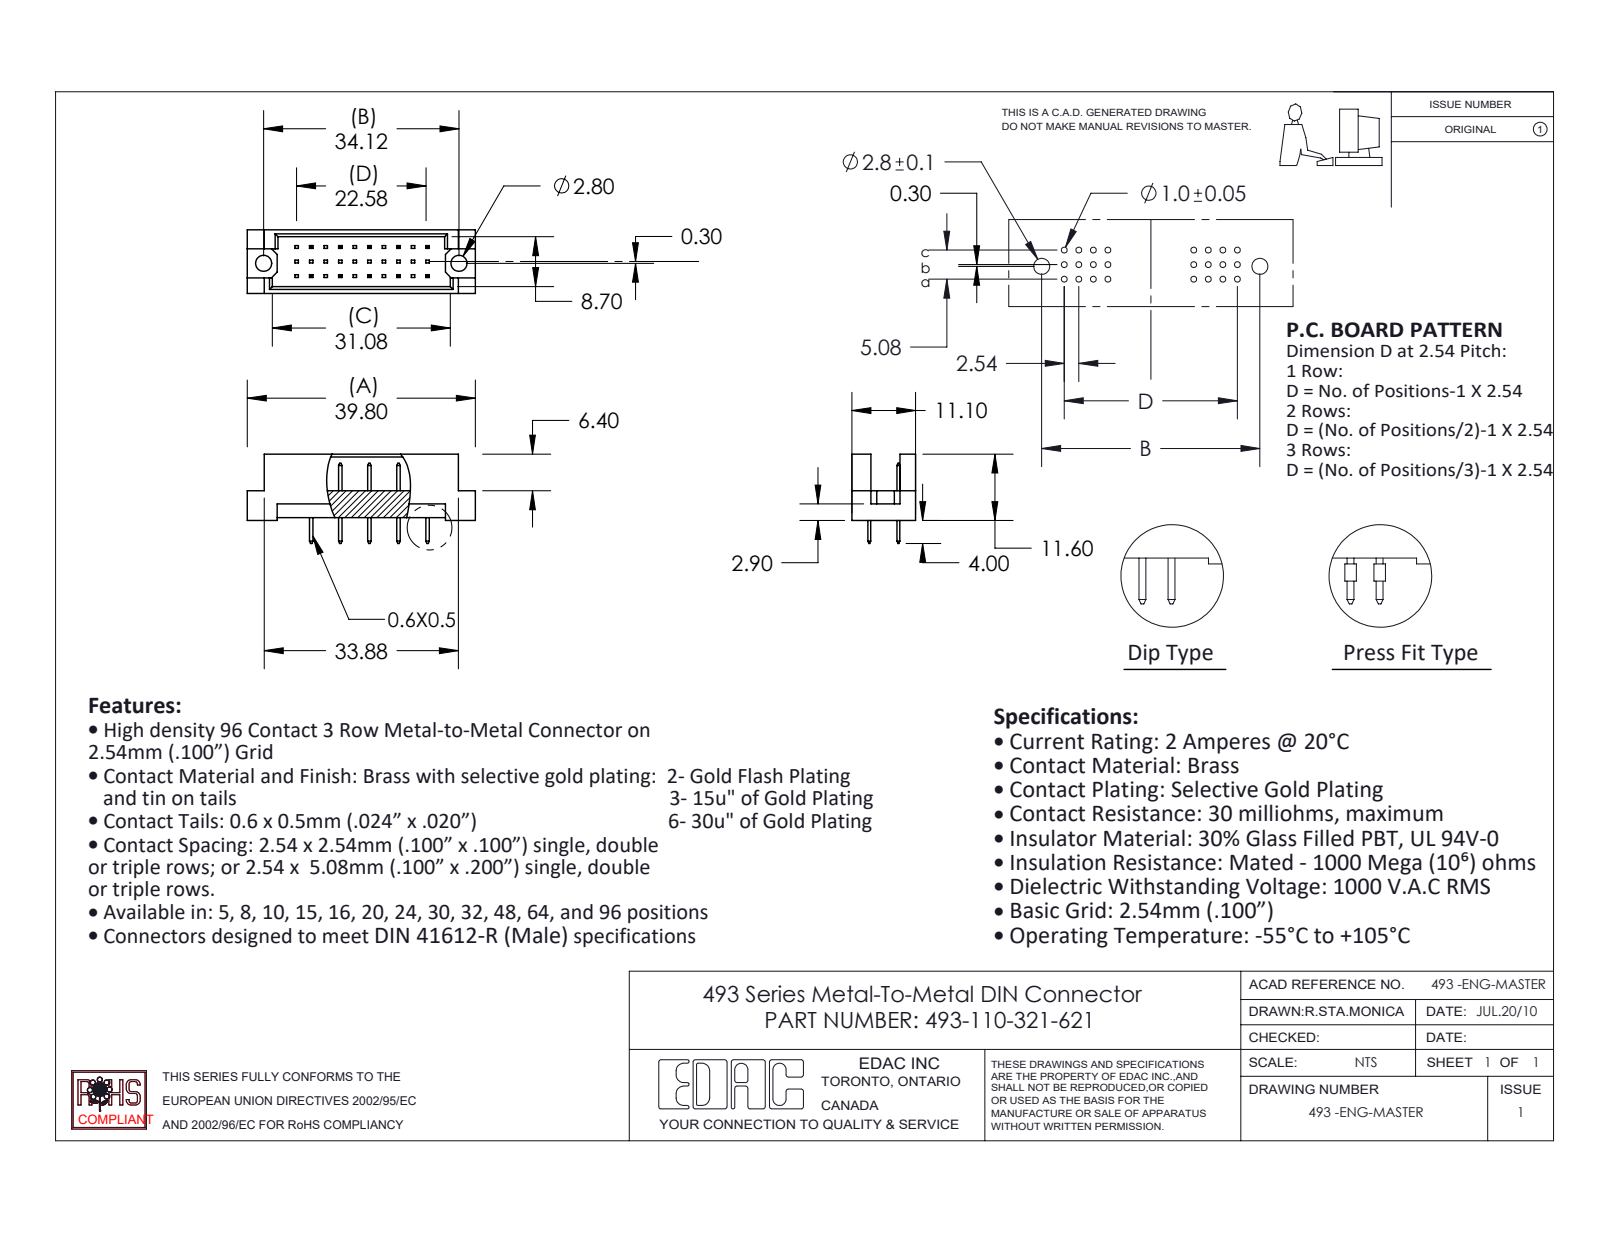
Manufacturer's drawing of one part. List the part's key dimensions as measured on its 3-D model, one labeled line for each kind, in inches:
Part name (STEP PRODUCT): 493-110-321-622; 493-290_21; 493 Part_30
STEP written by: SolidWorks 2020 (CONFIG_CONTROL_DESIGN)
Units: inches
Bodies: 11 solids, 312 faces (308 planar, 4 cylindrical, 0 other)
Overall size (bounding box): 1.567 × 0.614 × 0.437
Volume: 0.147 in³ · Surface area: 4.715 in²
Round holes (diameter × count): ⌀0.11 ×2
Main face-to-face distances: 0.047, 0.39, 0.437, 0.2, 0.343, 0.02, 0.185, 0.109, 0.128, 0.309
Hole centre spacings: 1.343
